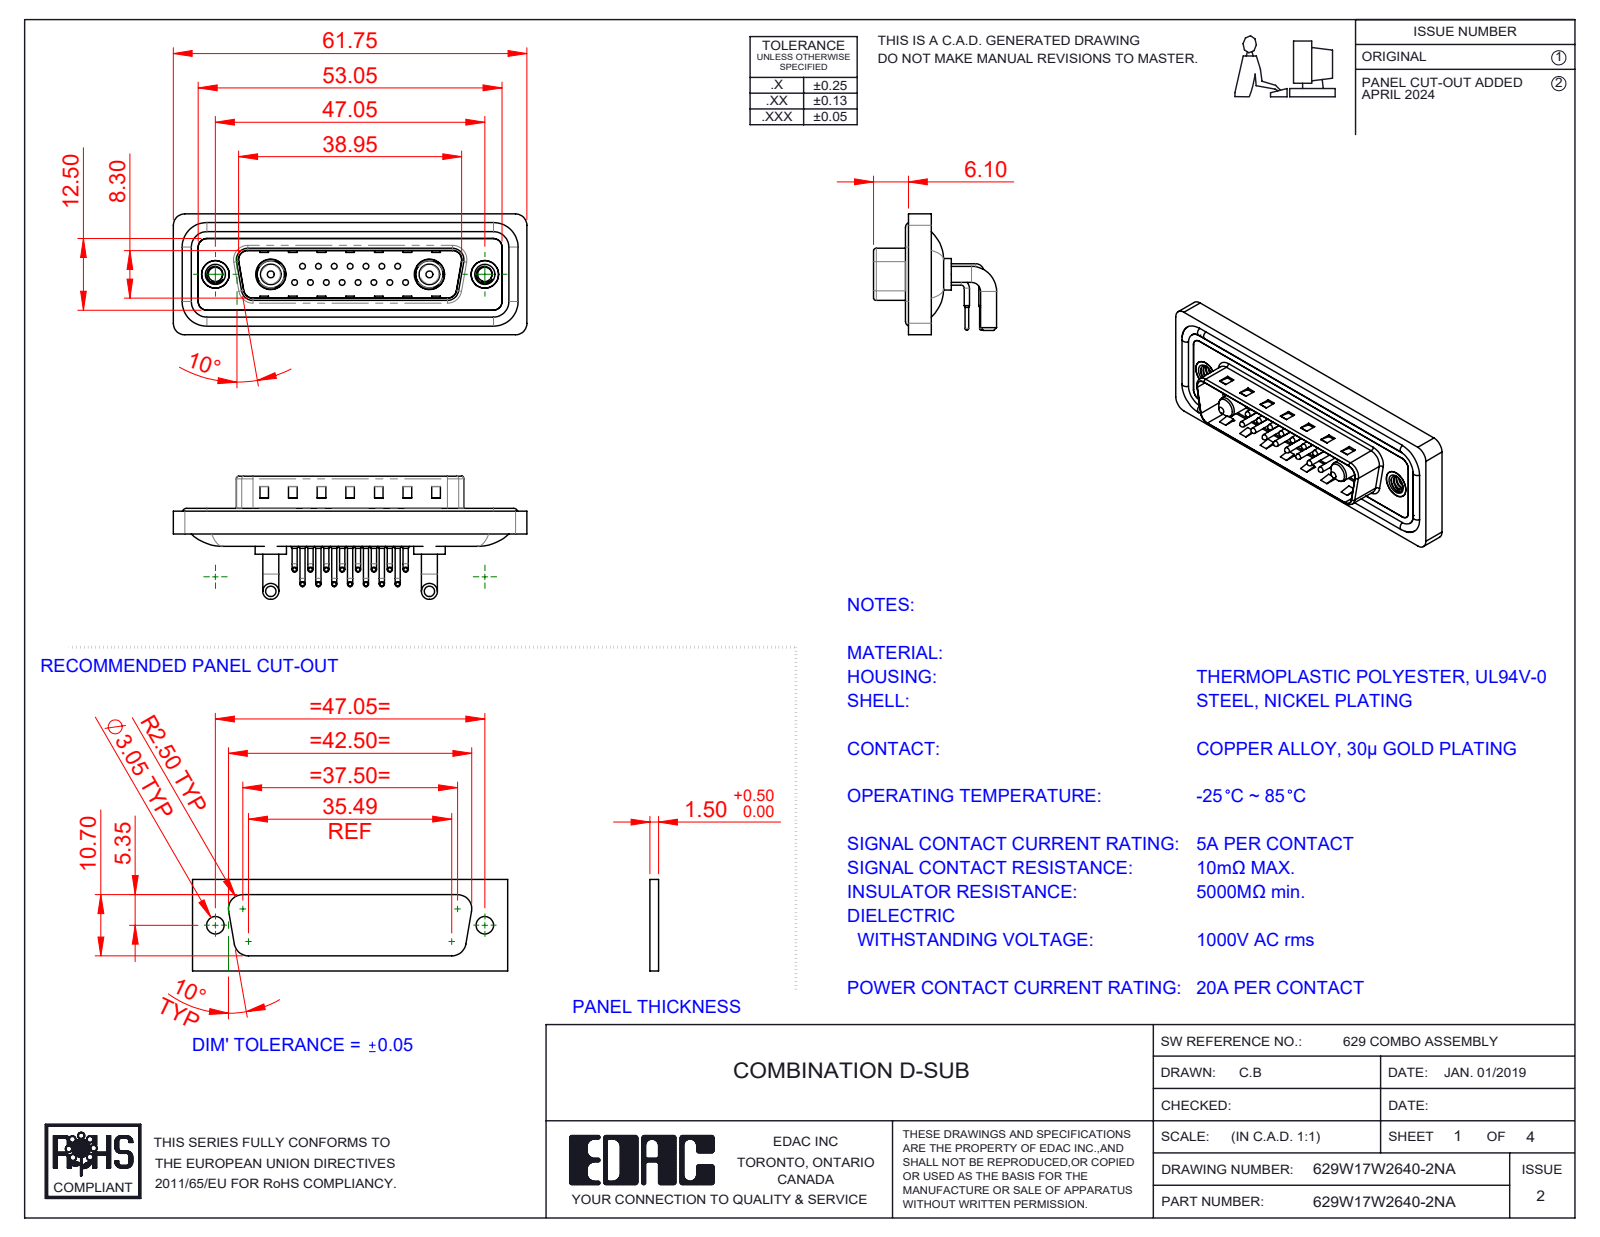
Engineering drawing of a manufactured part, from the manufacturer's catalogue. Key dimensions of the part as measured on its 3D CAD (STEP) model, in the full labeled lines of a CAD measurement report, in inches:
Part name (STEP PRODUCT): 629Combo Contact Row 2; 629Combo Contact Row 1; 629Combo Waterproof Housing_25 Contacts; 629Combo Housing_17W2 (+5 more)
STEP written by: SolidWorks 2023 (CONFIG_CONTROL_DESIGN)
Units: inches
Bodies: 26 solids, 2213 faces (1189 planar, 768 cylindrical, 256 other)
Overall size (bounding box): 2.431 × 0.846 × 0.831
Volume: 0.459 in³ · Surface area: 19.54 in²
Round holes (diameter × count): ⌀0.03 ×15, ⌀0.063 ×15, ⌀0.079 ×15, ⌀0.098 ×2, ⌀0.157 ×2, ⌀0.189 ×2, ⌀0.191 ×2, ⌀0.197 ×2, ⌀0.209 ×2
Round bosses / shafts (diameter × count): ⌀0.035 ×30, ⌀0.059 ×15, ⌀0.039 ×15, ⌀0.026 ×15, ⌀0.11 ×4, ⌀0.063 ×4, ⌀0.217 ×2, ⌀0.205 ×2
Partial cylindrical surfaces — rounded edges, fillets, slot ends (radius × count): R0.059 ×18, R0.079 ×18, R0.04 ×15, R0.02 ×8, R0.063 ×8, R0.01 ×4, R0.024 ×4, R0.026 ×4
Main face-to-face distances: 0.016, 0.114, 0.031, 0.161, 0.043, 0.083, 0.063, 0.177, 0.059, 0.098
Hole centre spacings: 0.124, 0.109, 0.218, 0.327, 0.198, 0.295, 0.436, 0.198
